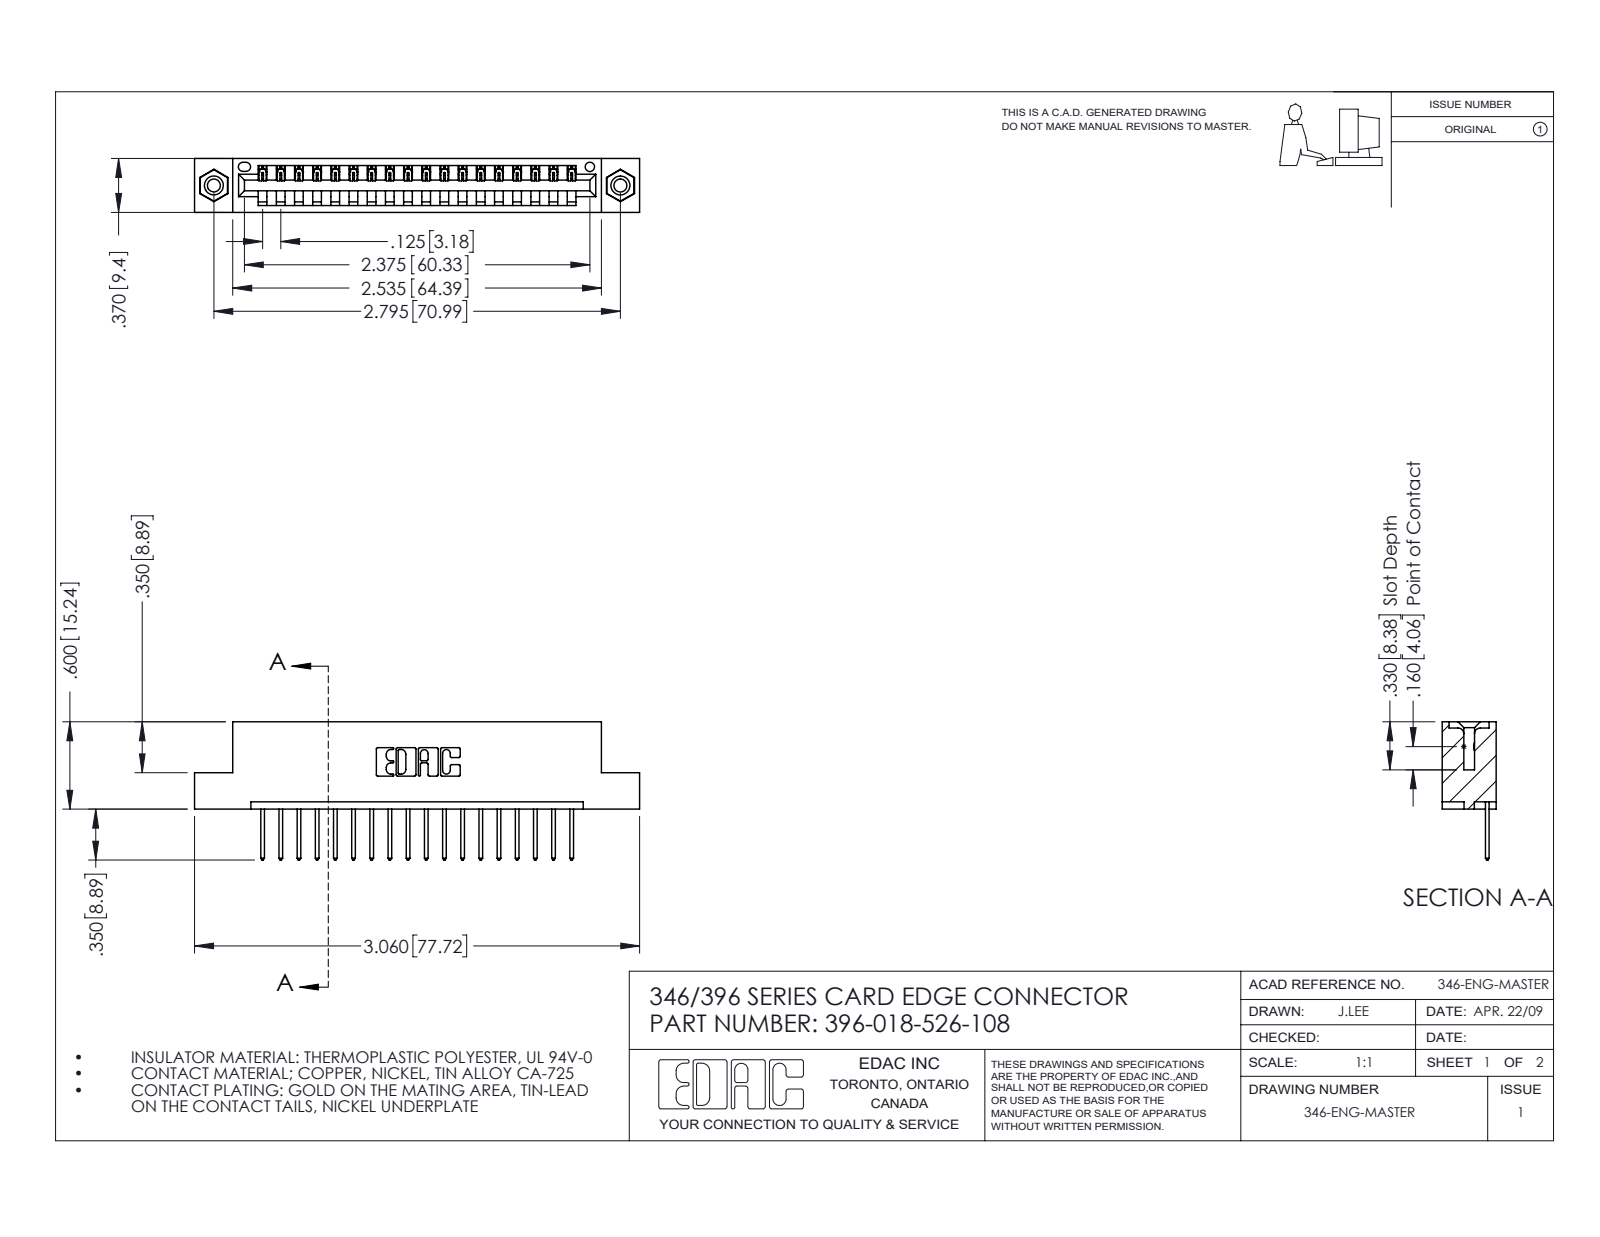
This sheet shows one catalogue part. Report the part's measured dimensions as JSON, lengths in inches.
{"part_name": "345-292-001_345-293-126; 346 Part_Flush Mounting Lugs - 0.156 Dia-TI; 345-250-001_345-250-003-102; 396-018-526-108", "step_written_by": "SolidWorks 2016 (CONFIG_CONTROL_DESIGN)", "units": "inches", "bodies": {"solids": 21, "faces": 1226, "planar": 828, "cylindrical": 382, "other": 16}, "overall_size": [3.06, 0.95, 0.37], "volume_in3": 0.443, "surface_area_in2": 13.66, "round_holes": [[0.089, 2], [0.125, 2], [0.156, 2], [0.064, 1]], "round_bosses_or_shafts": [[0.155, 2]], "partial_cylinders_radius": [[0.006, 36], [0.01, 36], [0.01, 22], [0.007, 6], [0.031, 6], [0.026, 3], [0.031, 2], [0.04, 2]], "face_to_face_distances": [0.048, 0.322, 0.25, 0.37, 0.072, 0.298, 0.025, 0.148, 0.222, 0.1], "hole_center_spacings": [0.246, 2.588, 2.795]}
